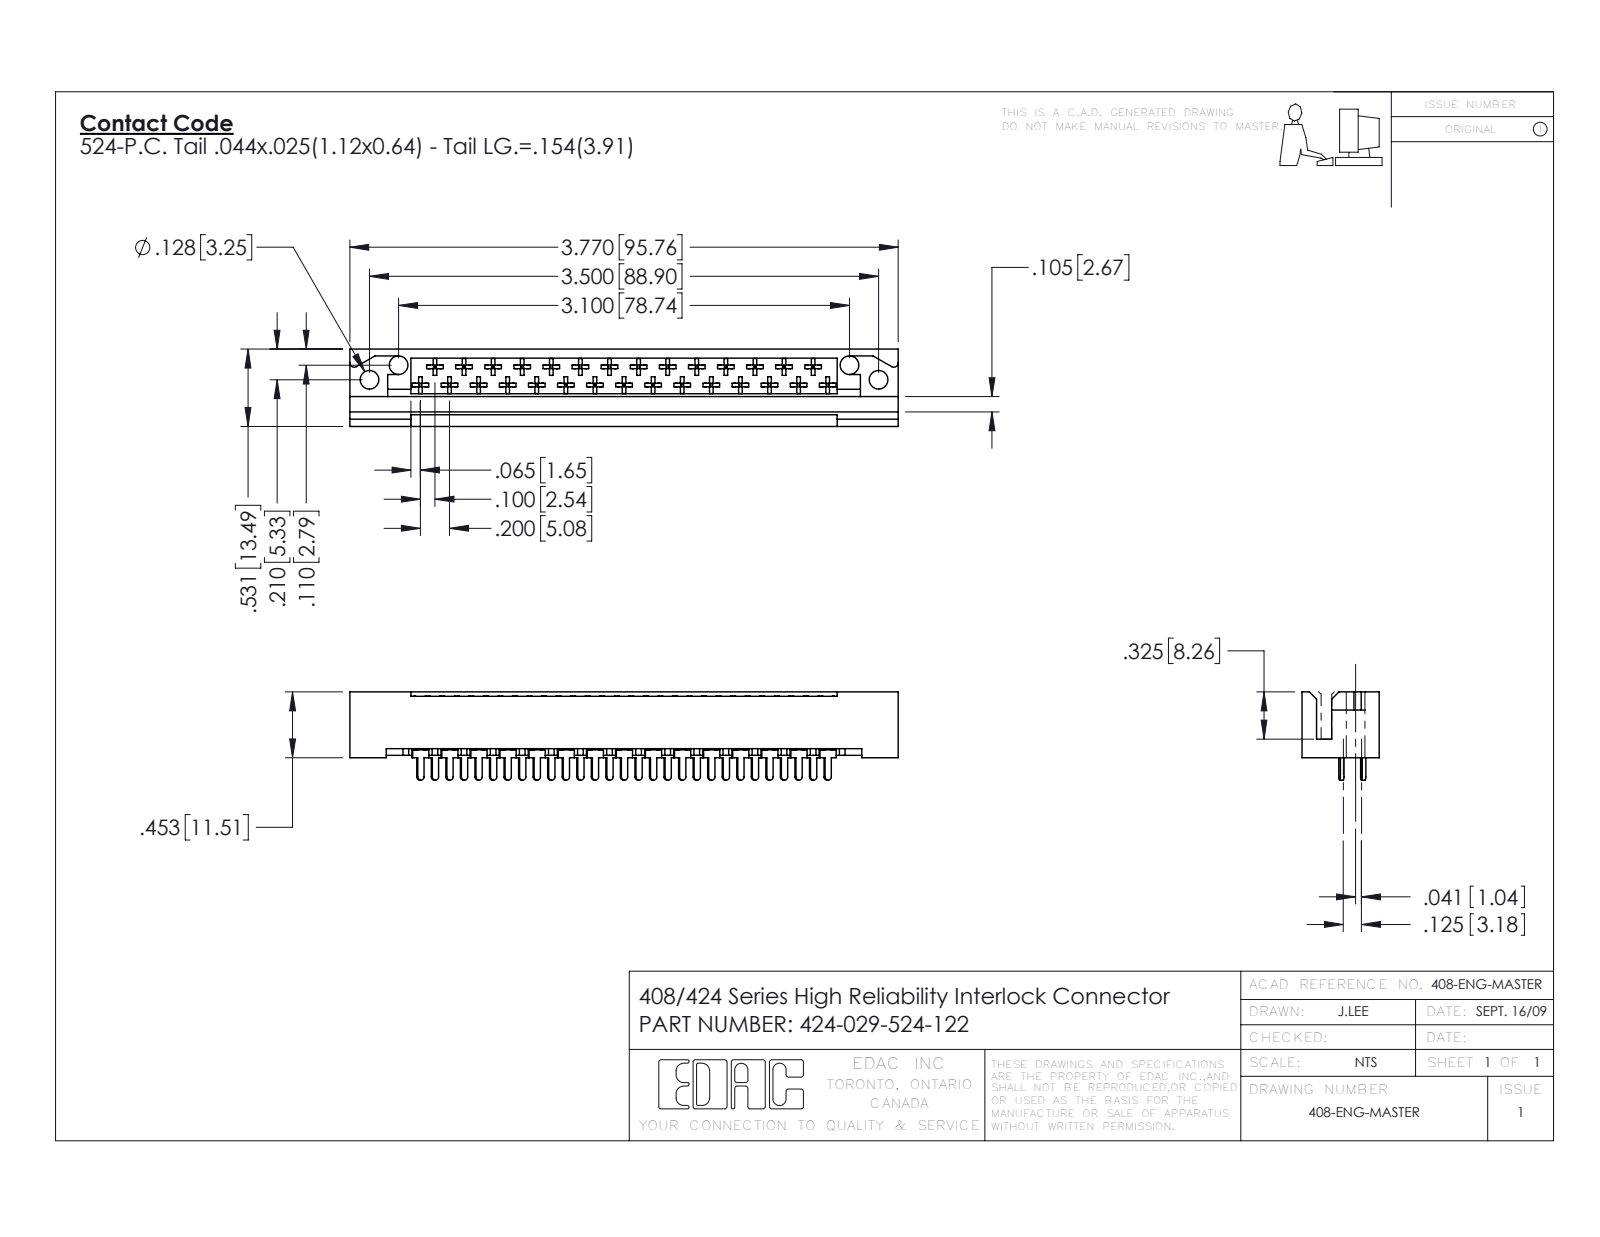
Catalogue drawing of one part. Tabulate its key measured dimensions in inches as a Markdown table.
| quantity | value |
| --- | --- |
| part name | 424 Part_029; 424-029-524-122; 408-290-001_408-290-124 - Top; 408-290-001_408-290-124 - Bottom |
| STEP written by | SolidWorks 2016 (CONFIG_CONTROL_DESIGN) |
| units | inches |
| bodies | 30 solids, 1657 faces (1264 planar, 277 cylindrical, 116 other) |
| overall size | 3.77 × 0.607 × 0.531 |
| volume | 0.603 in³ |
| surface area | 19.8 in² |
| round holes (diameter × count) | 0.128 × 4 |
| partial cylindrical surfaces (radius × count) | 0.01 × 174, 0.02 × 31, 0.022 × 29, 0.03 × 2 |
| main face-to-face distances | 0.1, 0.296, 0.025, 0.531, 0.125, 0.025, 0.431, 0.259, 0.172, 0.272 |
| hole center spacings | 0.224, 3.302, 3.1, 3.5 |
